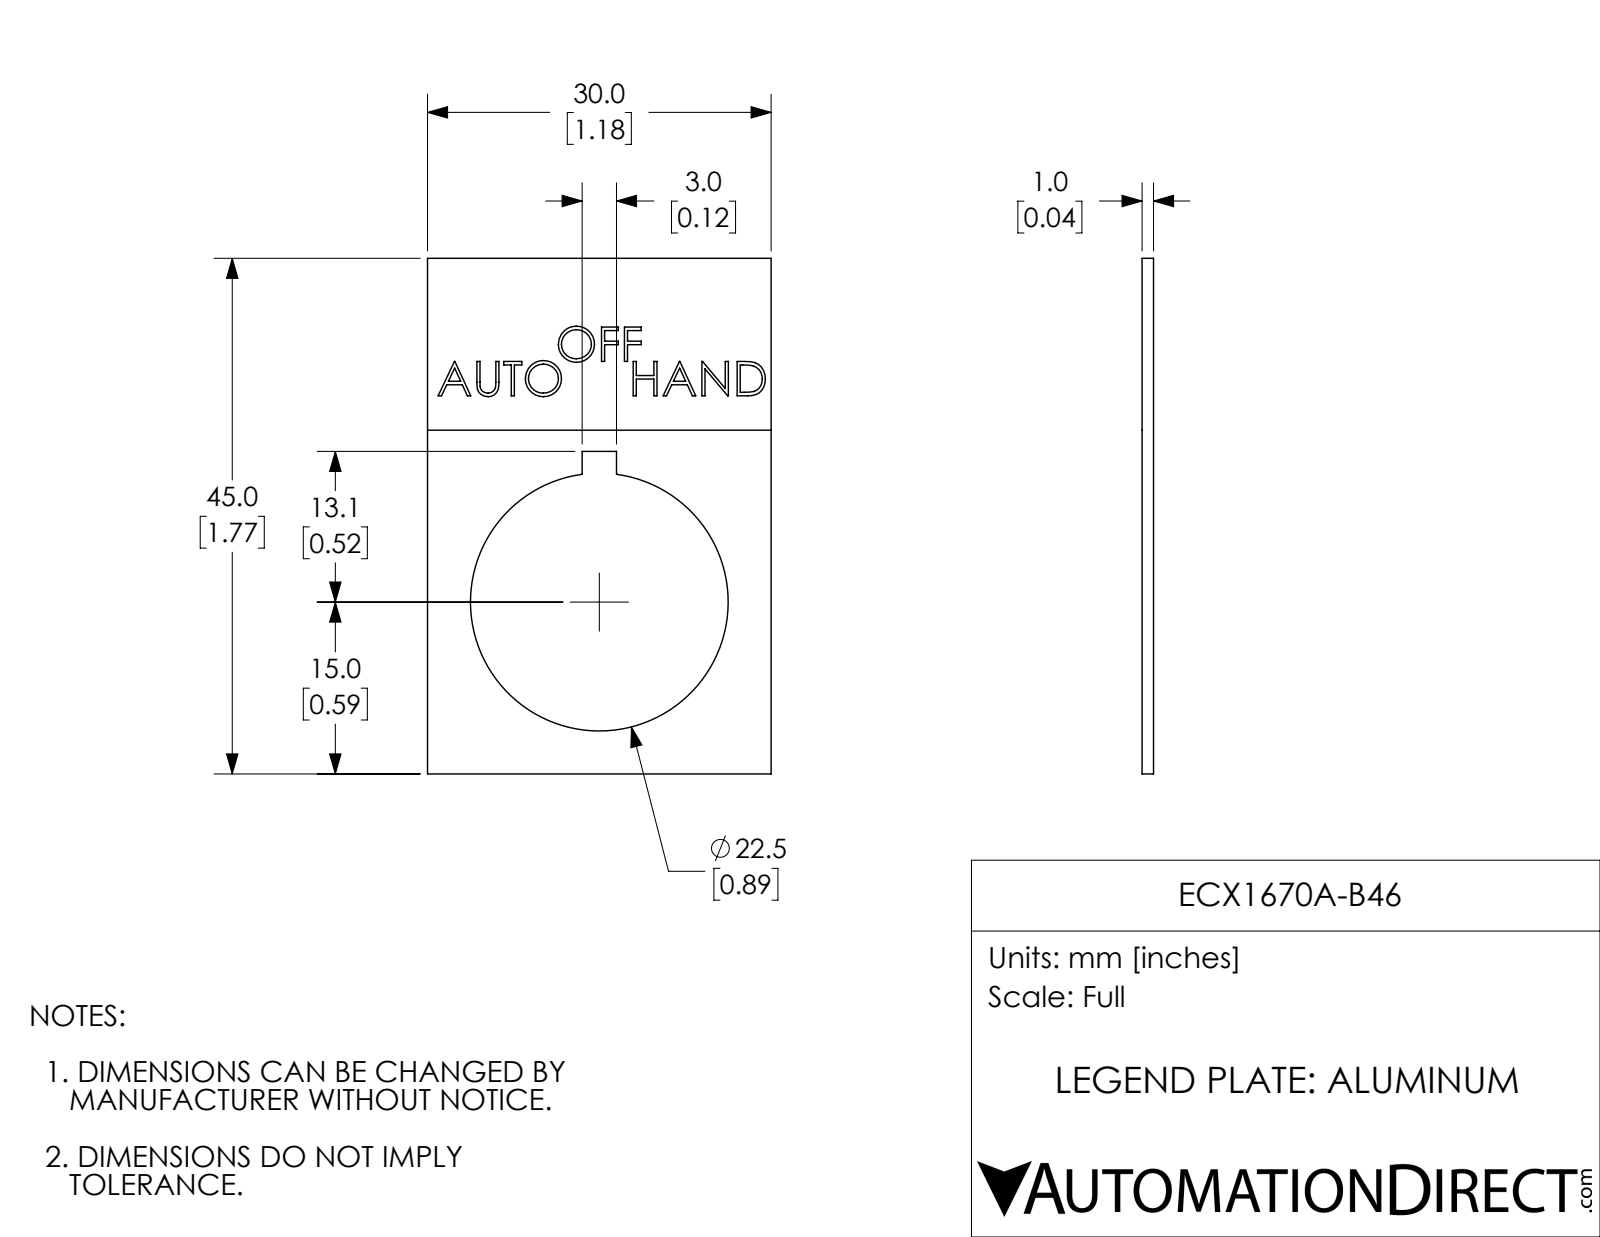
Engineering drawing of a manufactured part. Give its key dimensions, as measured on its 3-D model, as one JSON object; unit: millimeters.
{"part_name": "ECX1670A-B46", "step_written_by": "SolidWorks 2017 (AUTOMOTIVE_DESIGN)", "units": "millimeters", "bodies": {"solids": 1, "faces": 143, "planar": 110, "cylindrical": 3, "other": 30}, "overall_size": [45, 30, 1], "volume_mm3": 950, "surface_area_mm2": 2122, "round_holes": [[22.5, 1]], "face_to_face_distances": [1, 30, 45, 1, 13.5, 16.5, 28.1, 16.8, 3, 6]}
